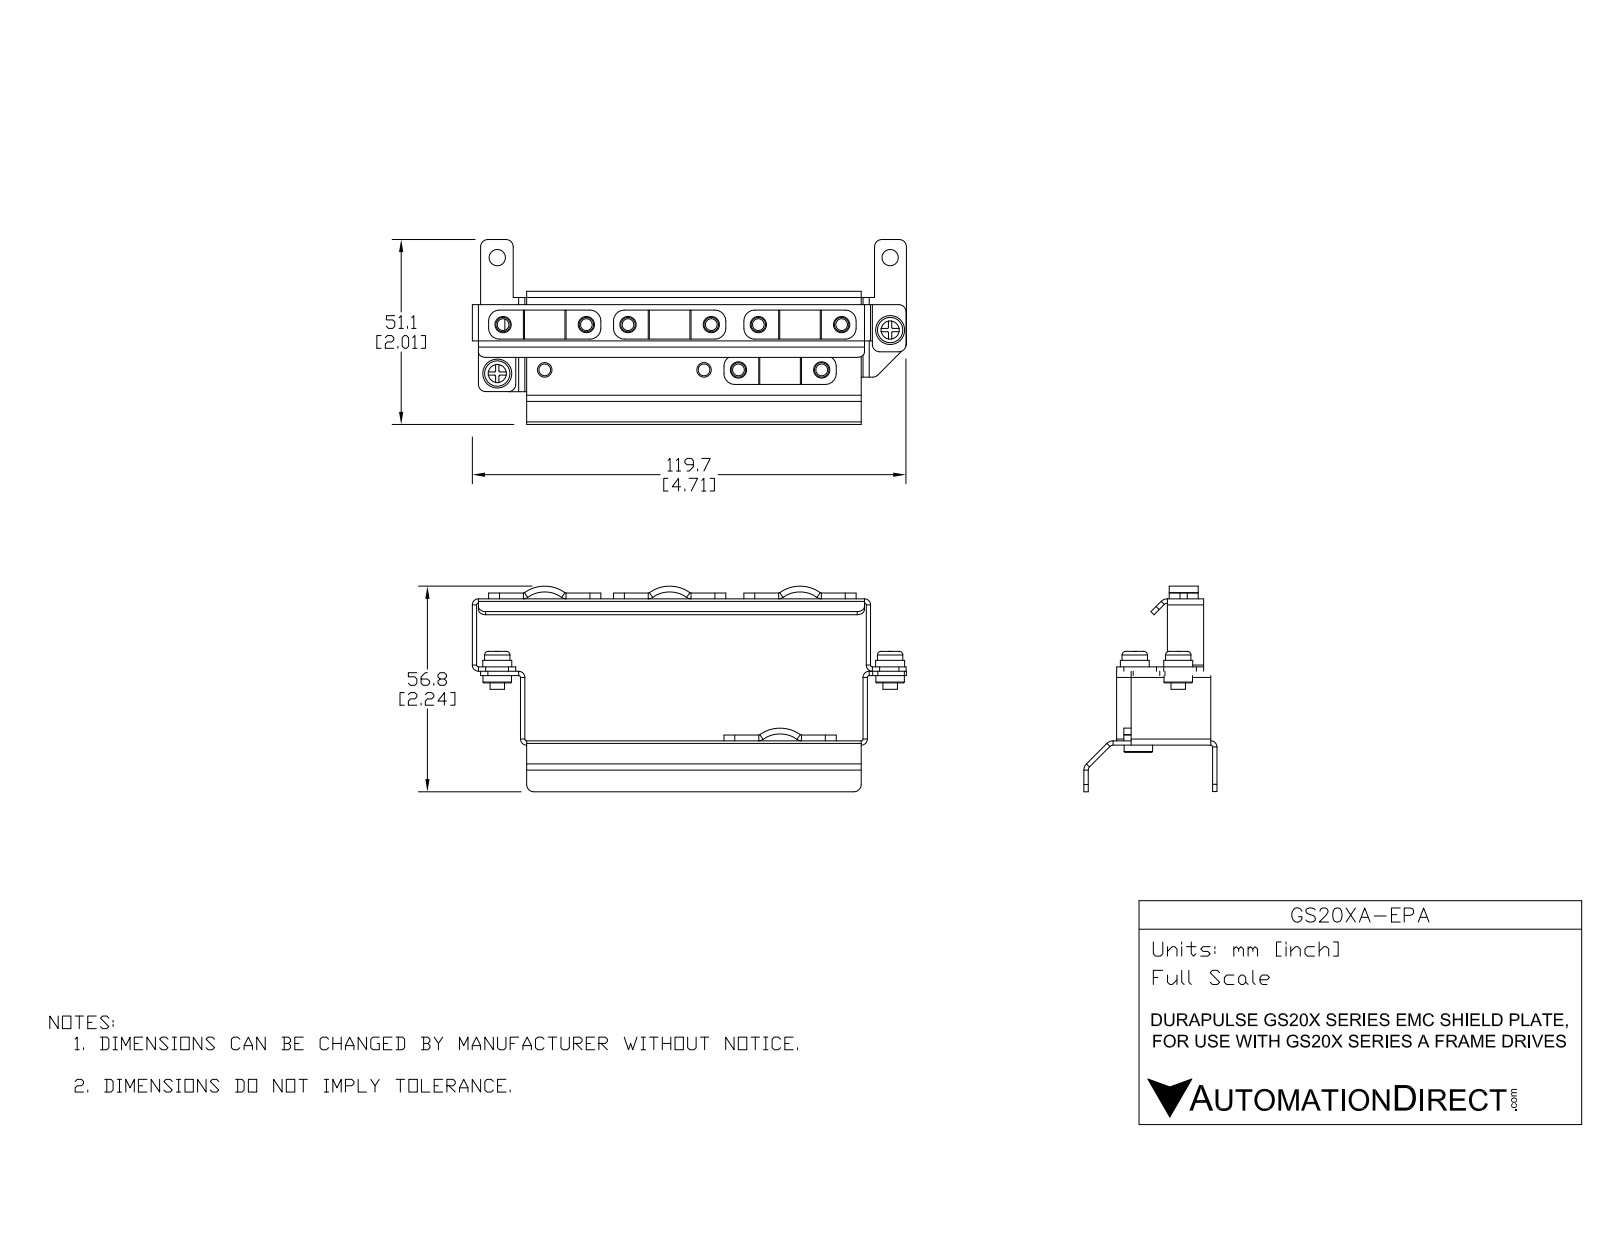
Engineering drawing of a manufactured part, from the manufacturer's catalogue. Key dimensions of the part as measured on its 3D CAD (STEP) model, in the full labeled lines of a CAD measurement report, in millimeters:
Part name (STEP PRODUCT): GS20XA-EPA
STEP written by: SolidWorks 2017 (AUTOMOTIVE_DESIGN)
Units: millimetres
Bodies: 11 solids, 511 faces (259 planar, 182 cylindrical, 70 other)
Overall size (bounding box): 119.9 × 56.8 × 51.1
Volume: 13 700 mm³ · Surface area: 23 940 mm²
Round holes (diameter × count): ⌀4.5 ×11, ⌀4 ×10, ⌀3.3 ×1
Round bosses / shafts (diameter × count): ⌀7 ×4, ⌀8 ×2, ⌀4 ×2, ⌀7.9 ×1, ⌀6.6 ×1, ⌀5.4 ×1
Partial cylindrical surfaces — rounded edges, fillets, slot ends (radius × count): R0.5 ×25, R2 ×20, R3 ×16, R1.7 ×9, R0.3 ×8, R2.1 ×8, R8 ×4, R9.6 ×4
Main face-to-face distances: 1.2, 39.2, 20.4, 20, 19.2, 18.8, 40.4, 35.6, 38, 17.1
Hole centre spacings: 23, 13.7, 33, 34.5, 36, 66.2, 70.5, 11.5
